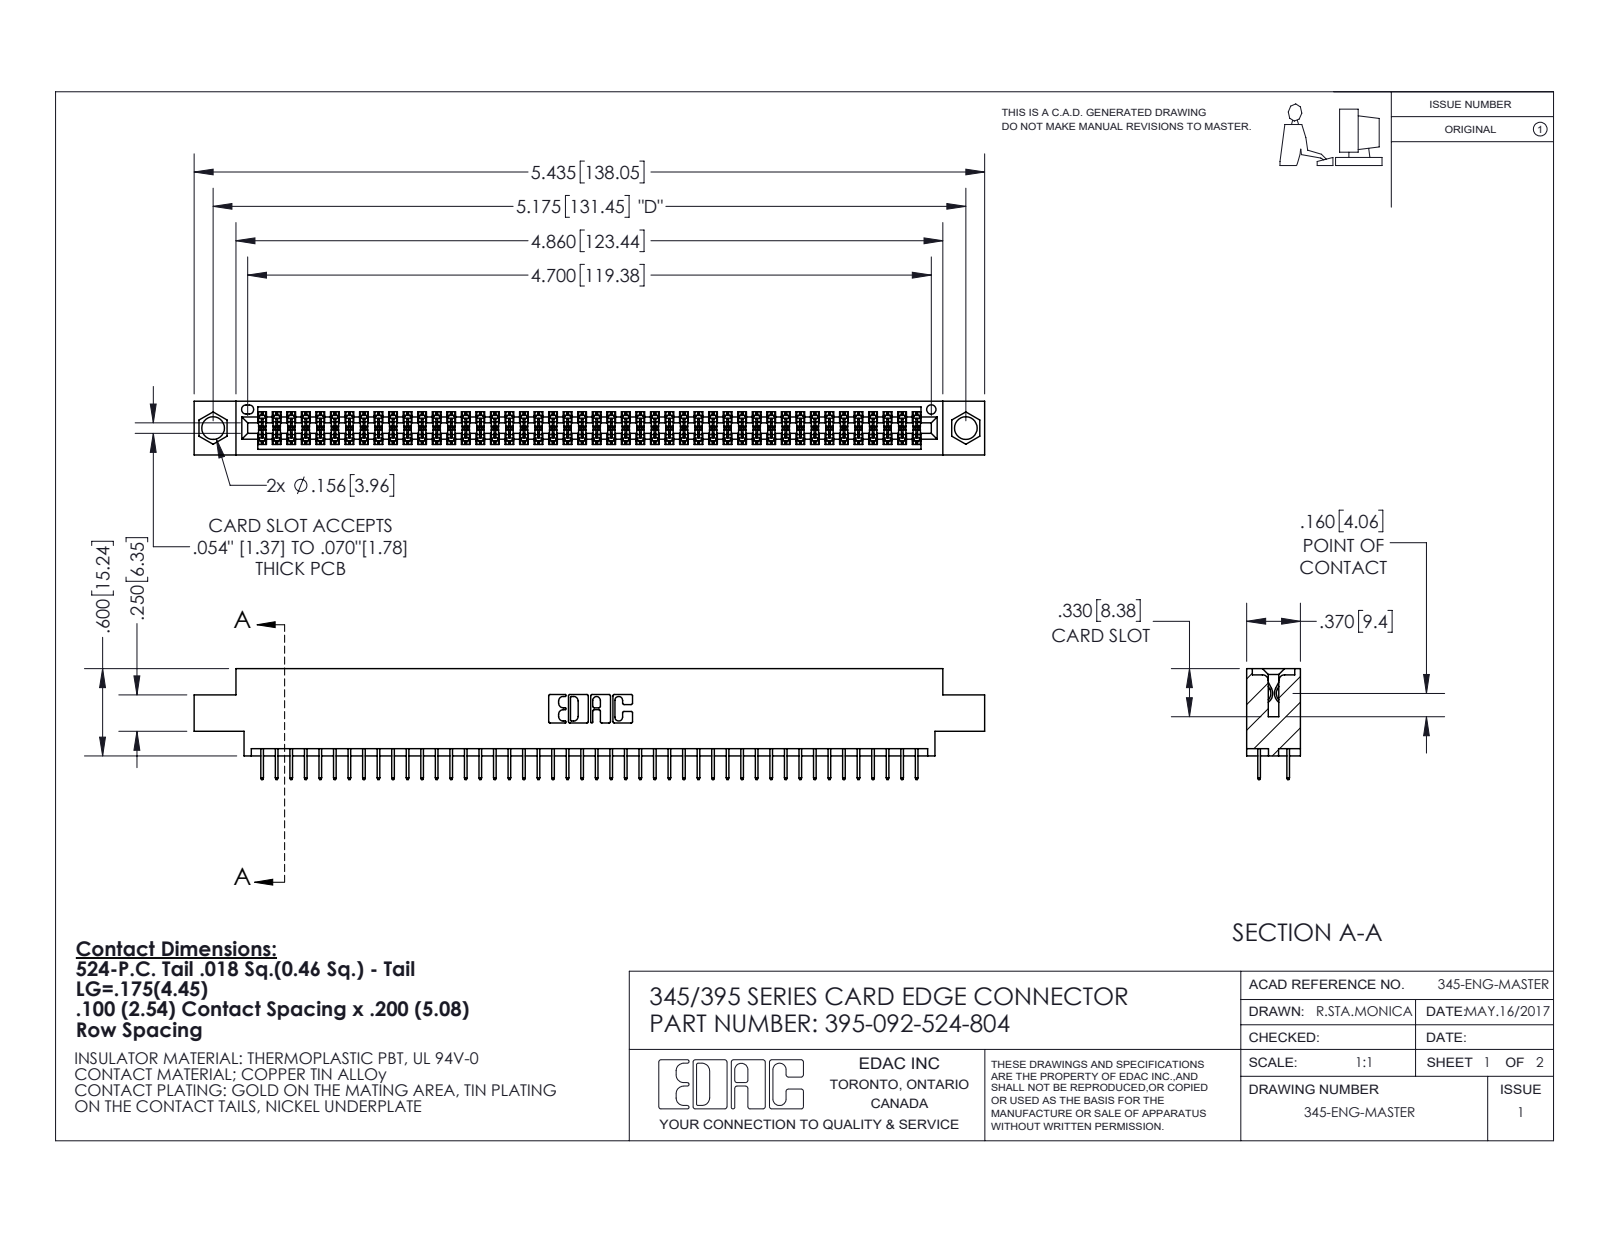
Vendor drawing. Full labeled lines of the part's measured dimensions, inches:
Part name (STEP PRODUCT): 345-292-001_345-293-124; 395-092-524-804; 345 Part_0.170 Offset - 0.156 Dia-TI
STEP written by: SolidWorks 2020 (CONFIG_CONTROL_DESIGN)
Units: inches
Bodies: 93 solids, 5112 faces (3686 planar, 1426 cylindrical, 0 other)
Overall size (bounding box): 5.435 × 0.762 × 0.37
Volume: 0.799 in³ · Surface area: 29.53 in²
Round holes (diameter × count): ⌀0.156 ×2, ⌀0.064 ×1
Partial cylindrical surfaces — rounded edges, fillets, slot ends (radius × count): R0.006 ×138, R0.01 ×22, R0.007 ×6, R0.031 ×6, R0.026 ×3, R0.014 ×2, R0.019 ×2, R0.022 ×2
Main face-to-face distances: 0.072, 0.298, 0.37, 0.2, 0.098, 0.272, 0.025, 0.225, 0.175, 0.072
Hole centre spacings: 0.27, 4.939, 5.175
